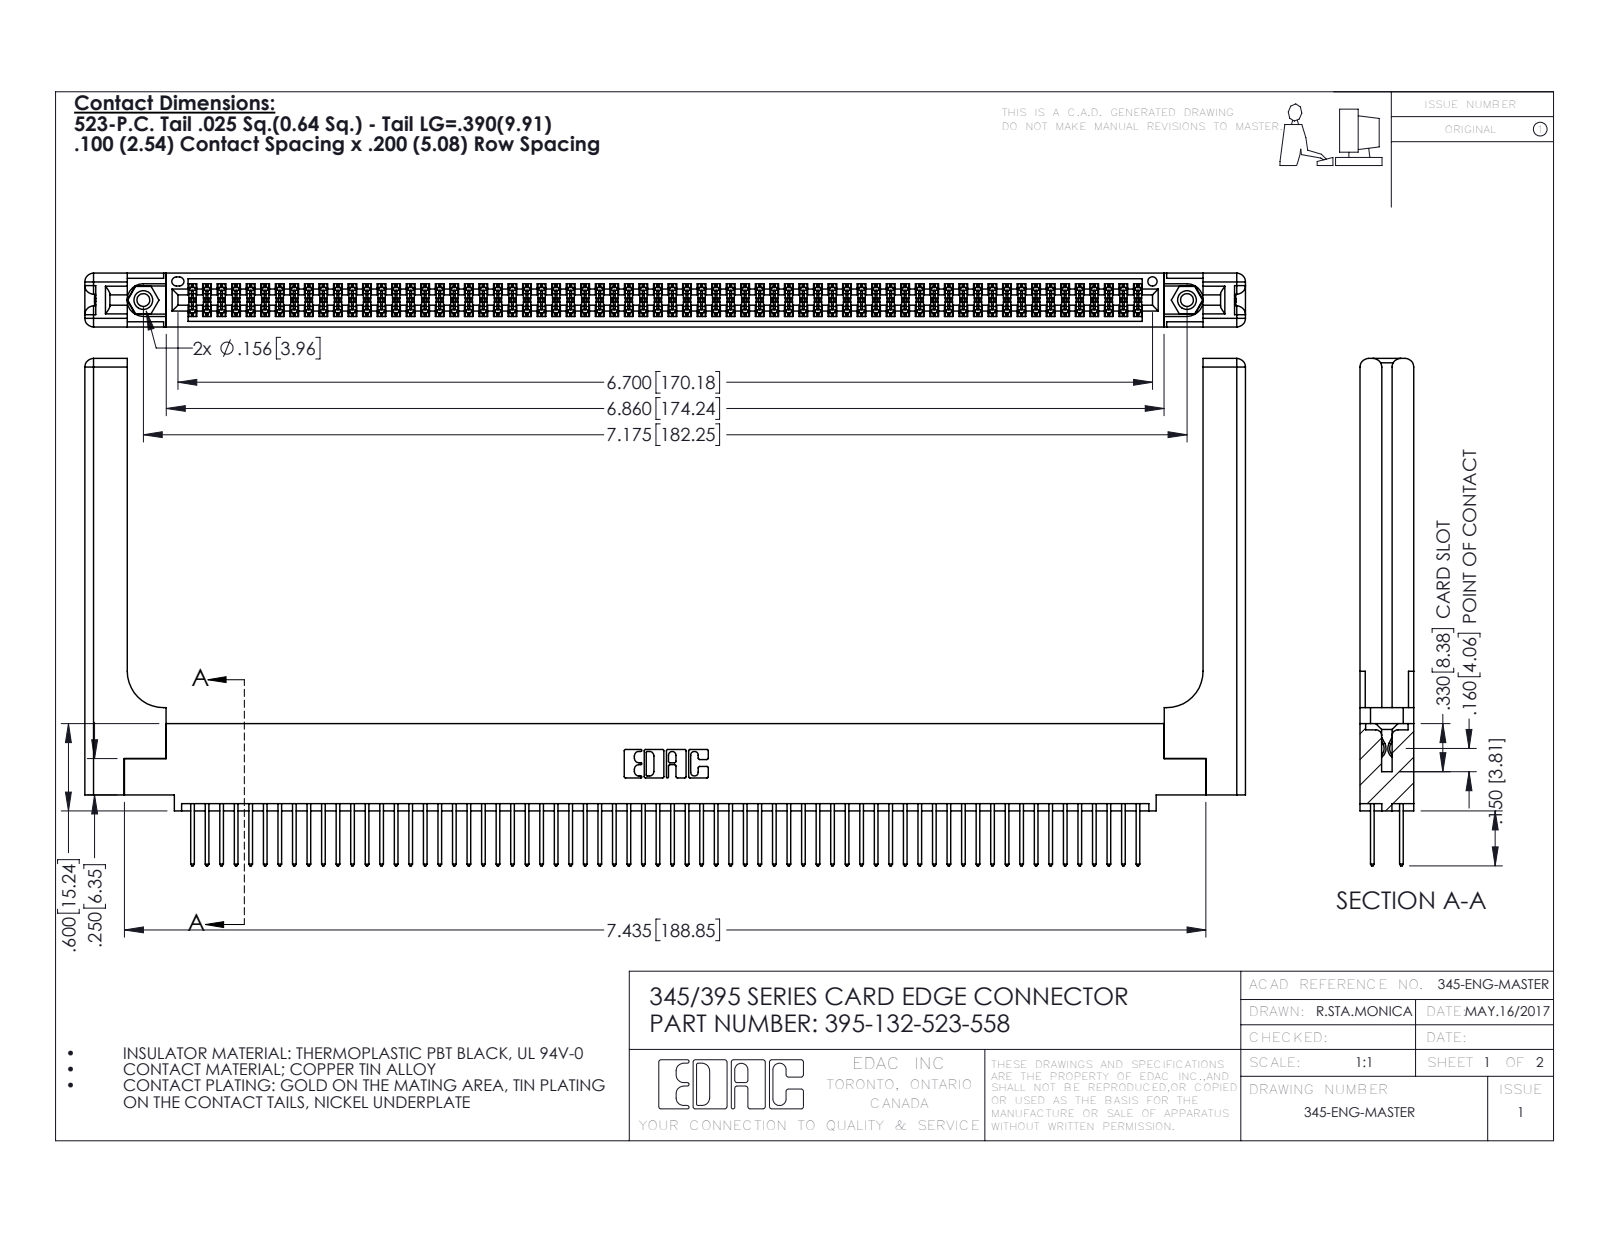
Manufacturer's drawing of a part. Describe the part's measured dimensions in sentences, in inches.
The part is named "345 Part_0.110 Offset - 0.156 Dia-TH; 345-292-001_345-293-123; 345-250-001_345-250-001-102; 345-220-058_345-220-058 (+1 more)". Its 3-D file was written by "SolidWorks 2016 (CONFIG_CONTROL_DESIGN)". It is 137 solids with 6986 faces: 4588 planar, 2338 cylindrical and 60 other. Overall it measures 7.979 by 3.487 by 0.37 inches. Its volume is 1.744 cubic inches and its surface area 56.66 square inches. Round holes: 2 of diameter 0.089, 2 of diameter 0.125, 2 of diameter 0.156, 1 of diameter 0.064. Round bosses or shafts: 2 of diameter 0.155. Partial cylindrical surfaces (rounded edges, fillets, slot ends): 198 of radius 0.006, 132 of radius 0.01, 22 of radius 0.01, 16 of radius 0.06, 6 of radius 0.007, 6 of radius 0.031, 3 of radius 0.026, 2 of radius 0.014. The main face-to-face distances are 0.072, 0.298, 0.37, 0.098, 0.272, 0.025, 0.2, 0.225, 0.175, 0.148. The hole center spacings are 0.27, 6.939, 7.175.
